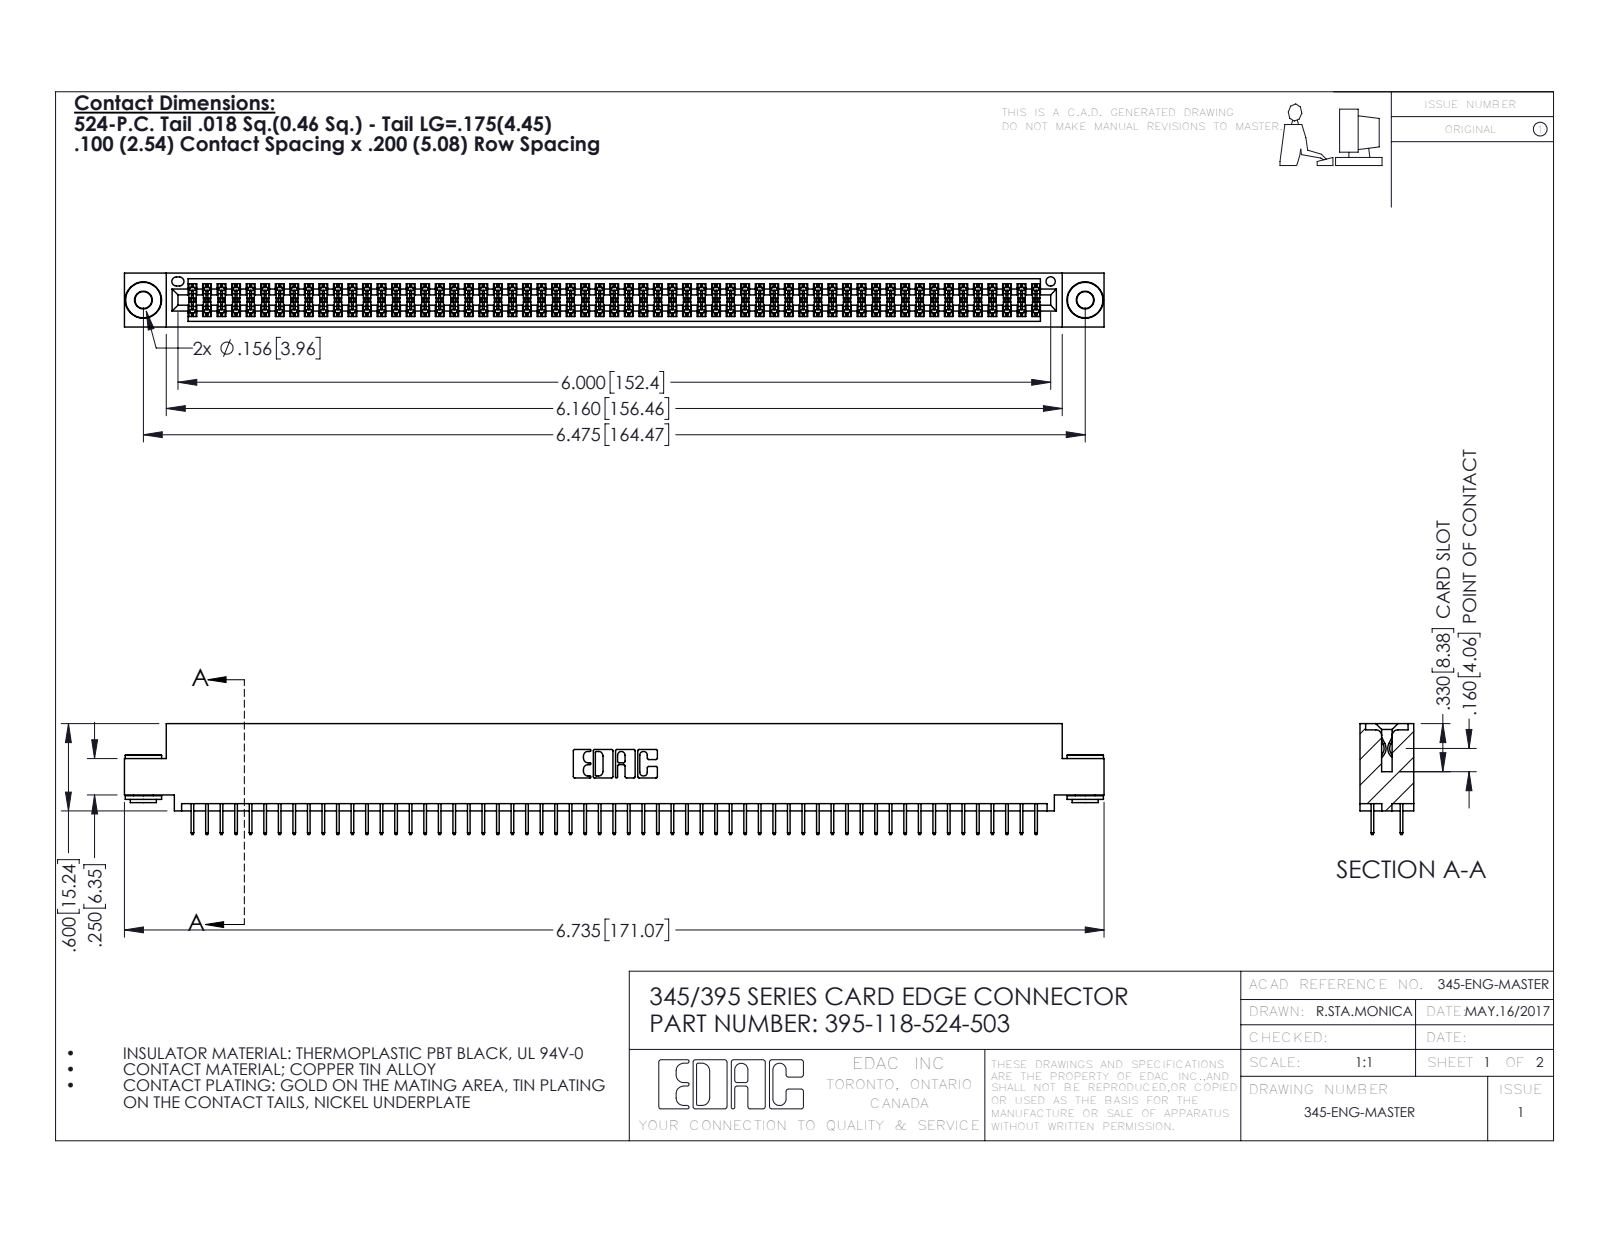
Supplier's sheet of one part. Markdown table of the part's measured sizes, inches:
| quantity | value |
| --- | --- |
| part name | 345-292-001_345-293-124; 345-250-002_345-250-002-102; 345 Part_0.110 Offset - 0.156 Dia-TH; 395-118-524-503 |
| STEP written by | SolidWorks 2016 (CONFIG_CONTROL_DESIGN) |
| units | inches |
| bodies | 121 solids, 6540 faces (4696 planar, 1836 cylindrical, 8 other) |
| overall size | 6.735 × 0.762 × 0.37 |
| volume | 1.01 in³ |
| surface area | 38.14 in² |
| round holes (diameter × count) | 0.116 × 2, 0.156 × 2, 0.064 × 1 |
| round bosses / shafts (diameter × count) | 0.25 × 2, 0.18 × 2, 0.136 × 2 |
| partial cylindrical surfaces (radius × count) | 0.006 × 177, 0.01 × 22, 0.007 × 6, 0.031 × 6, 0.026 × 3, 0.014 × 2, 0.019 × 2, 0.022 × 2 |
| main face-to-face distances | 0.072, 0.298, 0.2, 0.37, 0.025, 0.098, 0.272, 0.225, 0.072, 0.175 |
| hole center spacings | 0.27, 6.239, 6.475 |
